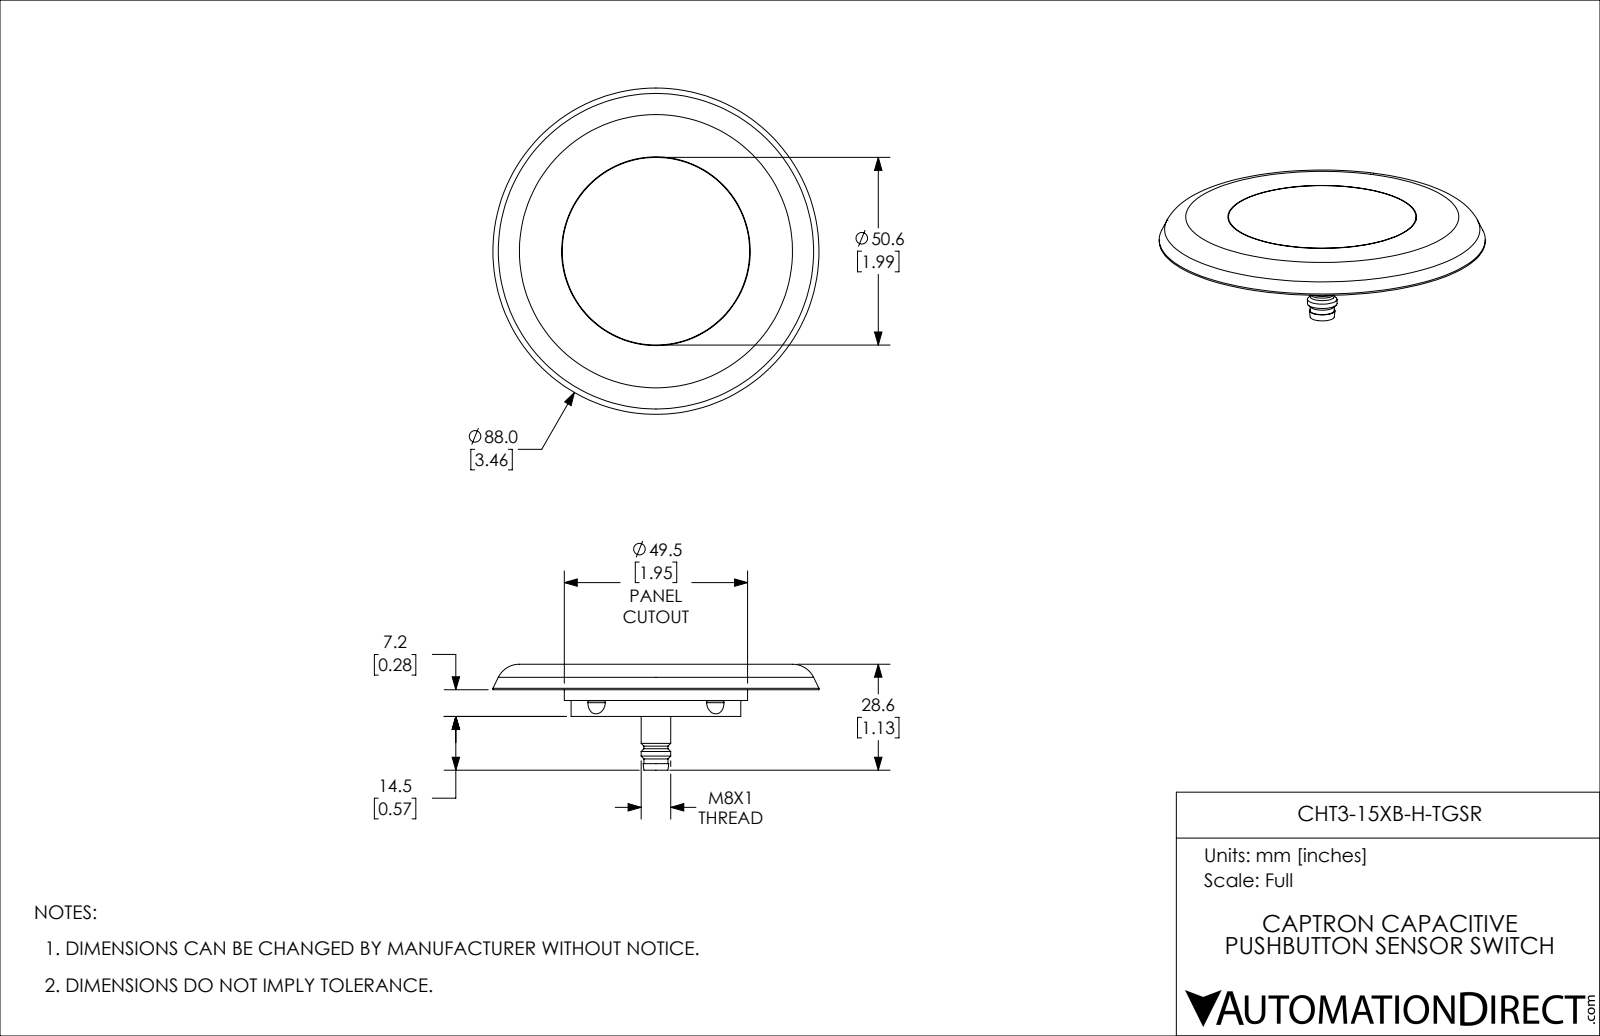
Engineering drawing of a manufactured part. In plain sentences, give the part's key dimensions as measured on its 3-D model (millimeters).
The part is named "CHT3-15XB-H-TGSR". Its 3-D file was written by "SolidWorks 2019 (CONFIG_CONTROL_DESIGN)". It is 10 solids with 90 faces: 25 planar, 40 cylindrical and 25 other. Overall it measures 88 by 88 by 28.6 millimeters. Its volume is 49 980 cubic millimeters and its surface area 21 720 square millimeters. Round holes: 1 of diameter 46.1, 1 of diameter 50.9. Round bosses or shafts: 5 of diameter 1, 1 of diameter 50.6, 1 of diameter 49.5, 1 of diameter 45.8, 1 of diameter 8, 1 of diameter 6.5. Partial cylindrical surfaces (rounded edges, fillets, slot ends): 4 of radius 5, 2 of radius 0.5, 1 of radius 0.9, 1 of radius 1, 1 of radius 2.9. The main face-to-face distances are 6.9, 4.6, 2.3, 7.2, 11.8, 14.1, 0.5, 4.3, 7.7, 2.9.
